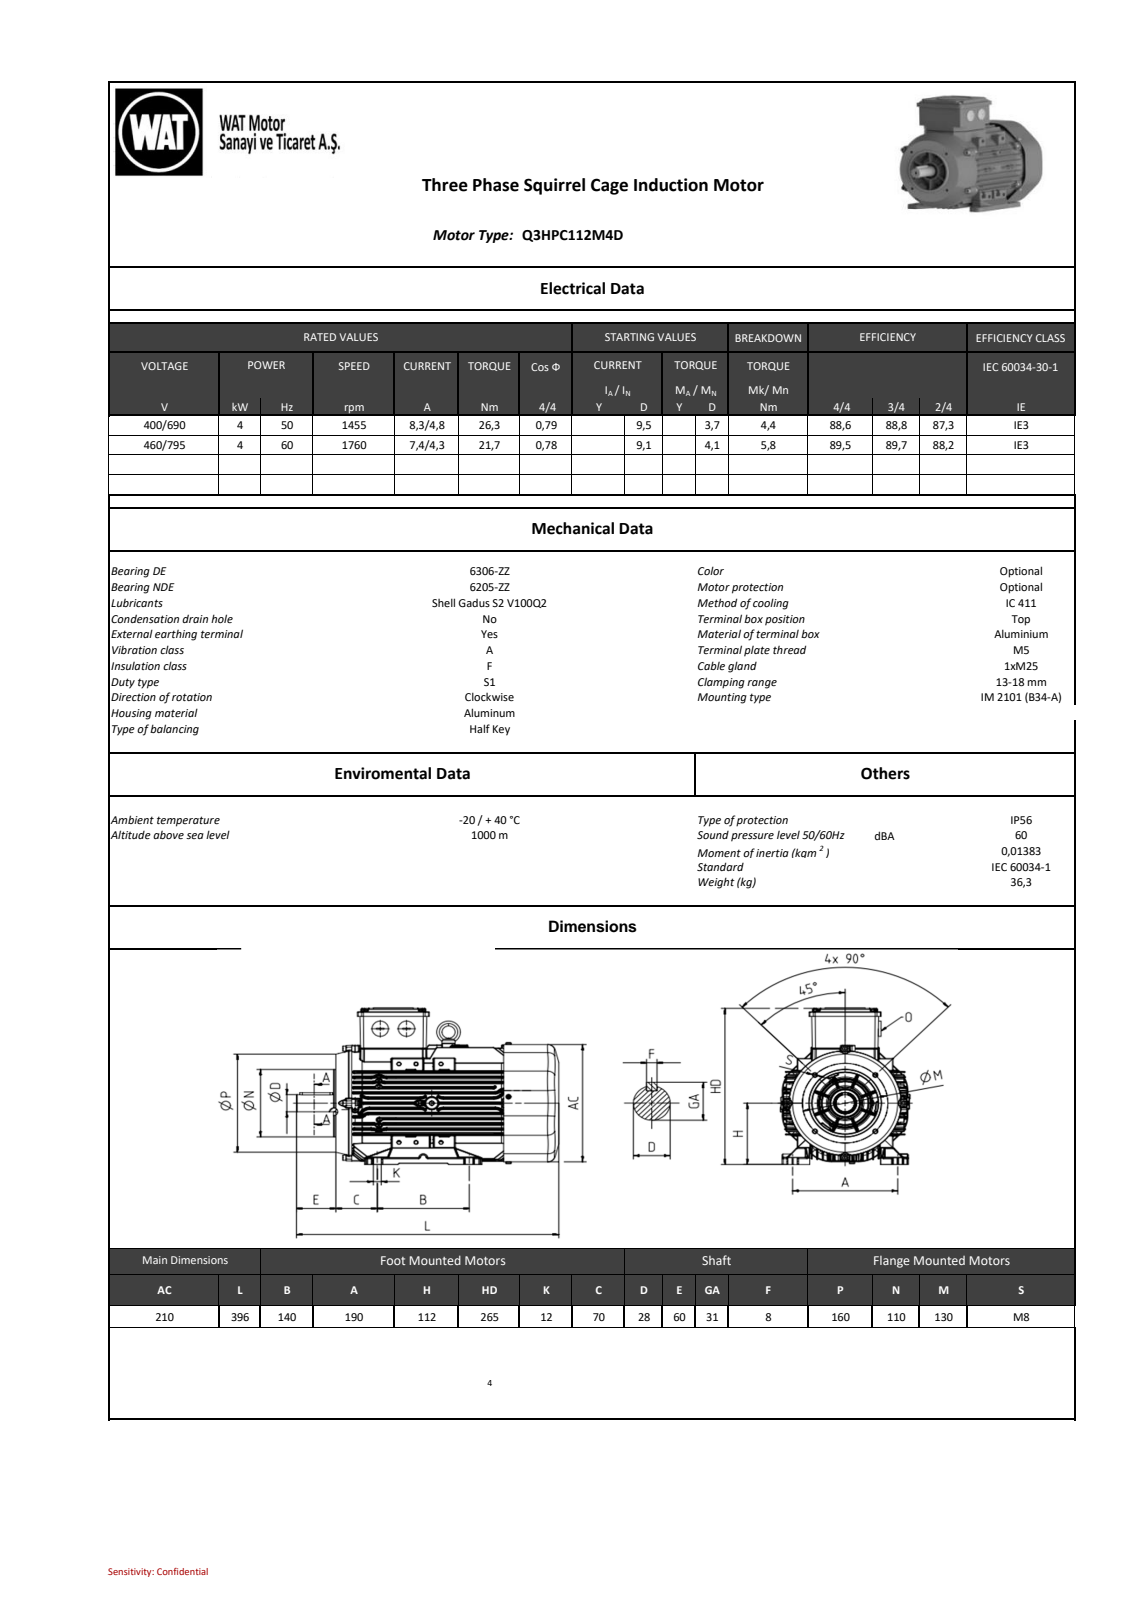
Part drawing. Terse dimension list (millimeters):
name: QH series_ 112_B34a_stp_objects
written by: SIEMENS PLM Software NX2206.8101 (AUTOMOTIVE_DESIGN)
unit: mm
bodies: 0 solids, 6976 faces (1580 planar, 2638 cylindrical, 2758 other)
size: 396 × 274.5 × 225.11
holes: 2× ⌀4.6, 1× ⌀8, 1× ⌀8.5, 1× ⌀47
bosses: 4× ⌀13, 4× ⌀10, 4× ⌀8, 3× ⌀14.8, 2× ⌀25, 2× ⌀6, 1× ⌀188, 1× ⌀110
rounds: 563× R2, 496× R0.8, 308× R1, 304× R0.5, 90× R1.2, 64× R3, 12× R4, 12× R6
face distances: 1, 21.5, 10.99, 35.96, 99.54, 24.97, 8.16, 112.88, 89.87, 68.93
